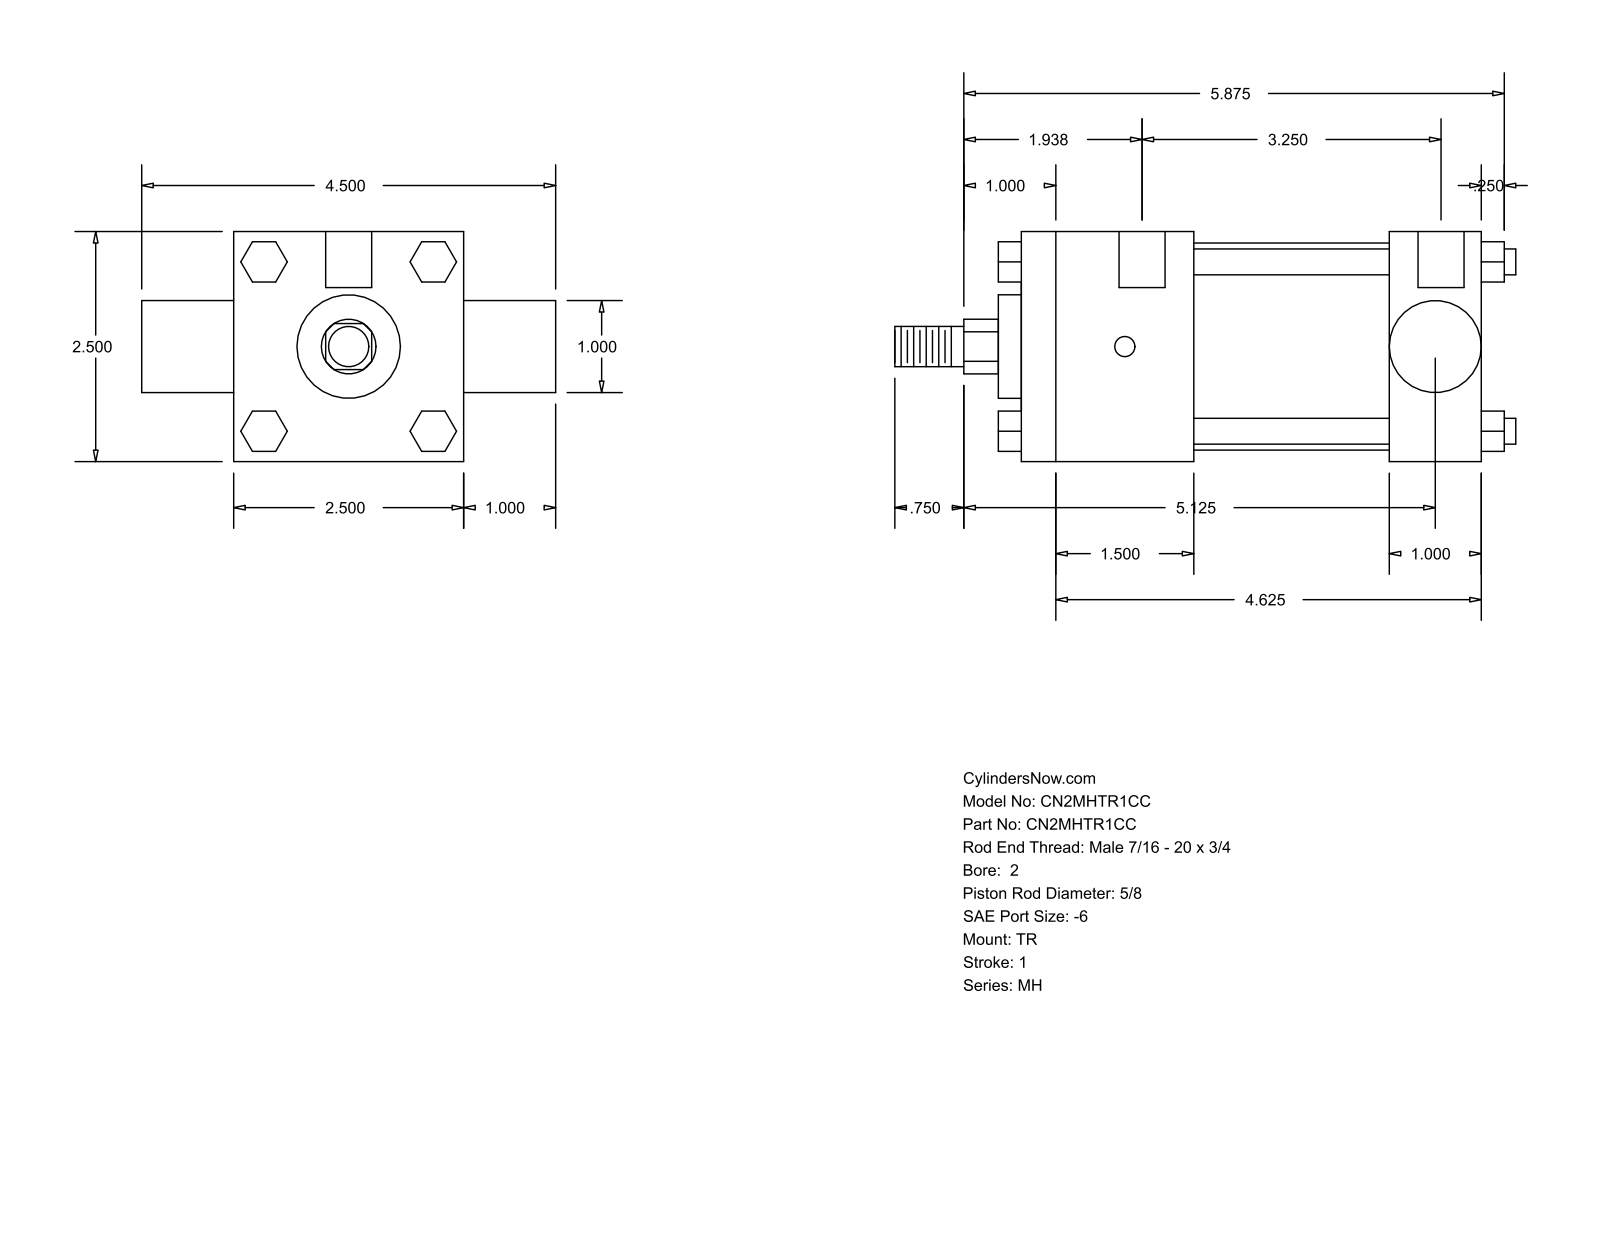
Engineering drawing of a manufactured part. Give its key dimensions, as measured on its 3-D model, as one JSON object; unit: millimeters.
{"part_name": "MH_TR__0200_0.625", "step_written_by": "GSSL Pune (CONFIG_CONTROL_DESIGN)", "units": "millimeters", "bodies": {"solids": 0, "faces": 120, "planar": 92, "cylindrical": 28, "other": 0}, "overall_size": [171.45, 114.3, 63.5], "round_holes": [[5.56, 3], [12.7, 2]], "round_bosses_or_shafts": [[7.14, 4], [57.15, 1], [28.57, 1], [25.35, 1], [15.88, 1], [11.11, 1]], "partial_cylinders_radius": [[7.54, 1]], "face_to_face_distances": [63.5, 127, 53.97, 47.62, 101.59, 79.38, 25.41, 25.4, 88.9, 6.35], "hole_center_spacings": [3.18, 4.76, 82.55, 85.73, 87.31, 90.49]}
